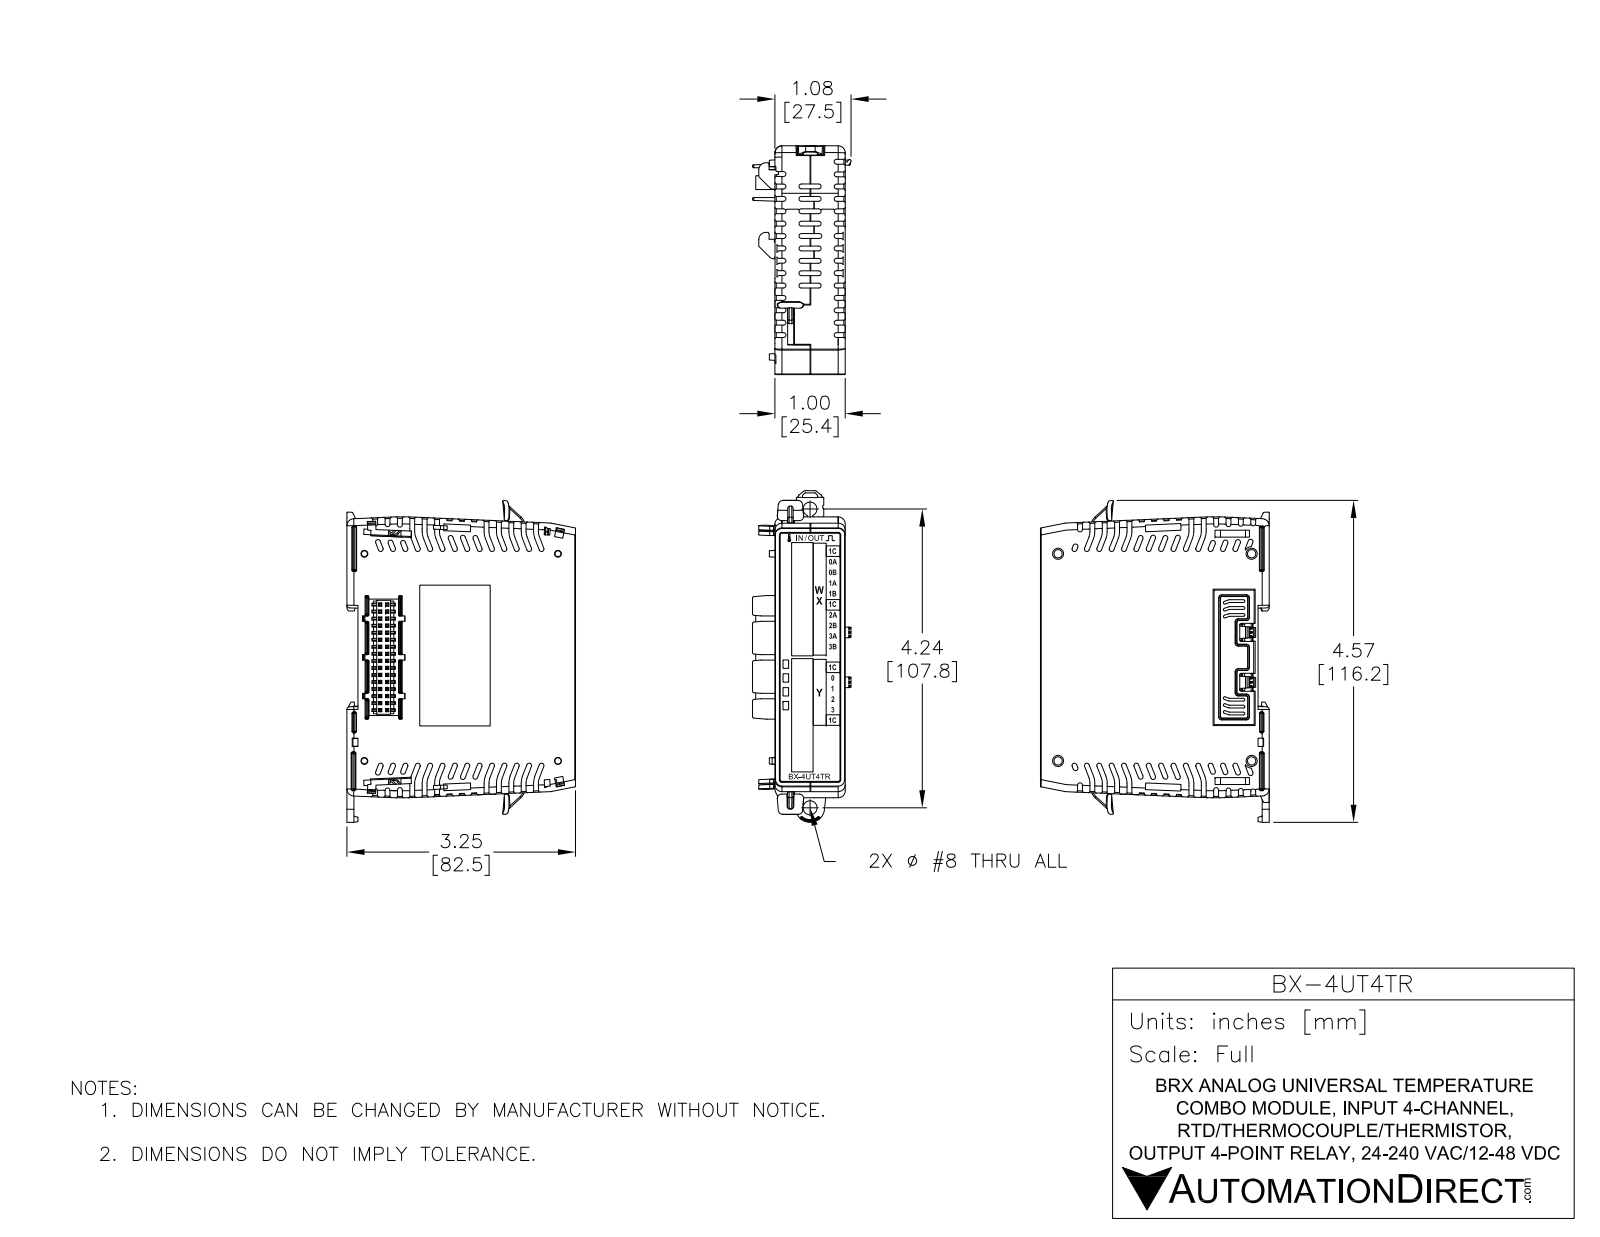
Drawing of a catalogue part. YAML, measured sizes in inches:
part_name: "BX-4UT4TR"
step_written_by: "SolidWorks 2017 (AUTOMOTIVE_DESIGN)"
units: inches
bodies: {solids: 16, faces: 4172, planar: 2931, cylindrical: 672, other: 569}
overall_size: [4.586, 3.25, 1.402]
volume: 11.58
surface_area: 72.51
round_holes:
  - {diameter: 0.047, count: 2}
  - {diameter: 0.065, count: 2}
  - {diameter: 0.118, count: 2}
  - {diameter: 0.118, count: 2}
  - {diameter: 0.04, count: 1}
  - {diameter: 0.199, count: 1}
round_bosses_or_shafts:
  - {diameter: 0.062, count: 2}
  - {diameter: 0.059, count: 2}
  - {diameter: 0.044, count: 1}
  - {diameter: 0.036, count: 1}
partial_cylinders:
  - {radius: 0.005, count: 102}
  - {radius: 0.008, count: 101}
  - {radius: 0.01, count: 47}
  - {radius: 0.02, count: 34}
  - {radius: 0.005, count: 24}
  - {radius: 0.062, count: 20}
  - {radius: 0.117, count: 14}
  - {radius: 0.039, count: 13}
face_to_face_distances: [1, 3.211, 3.22, 0.475, 0.039, 0.157, 3.053, 3.063, 0.078, 0.1]
hole_center_spacings: [0.1, 0.824, 0.919, 1.3, 2.093, 2.193, 2.585, 2.617]
